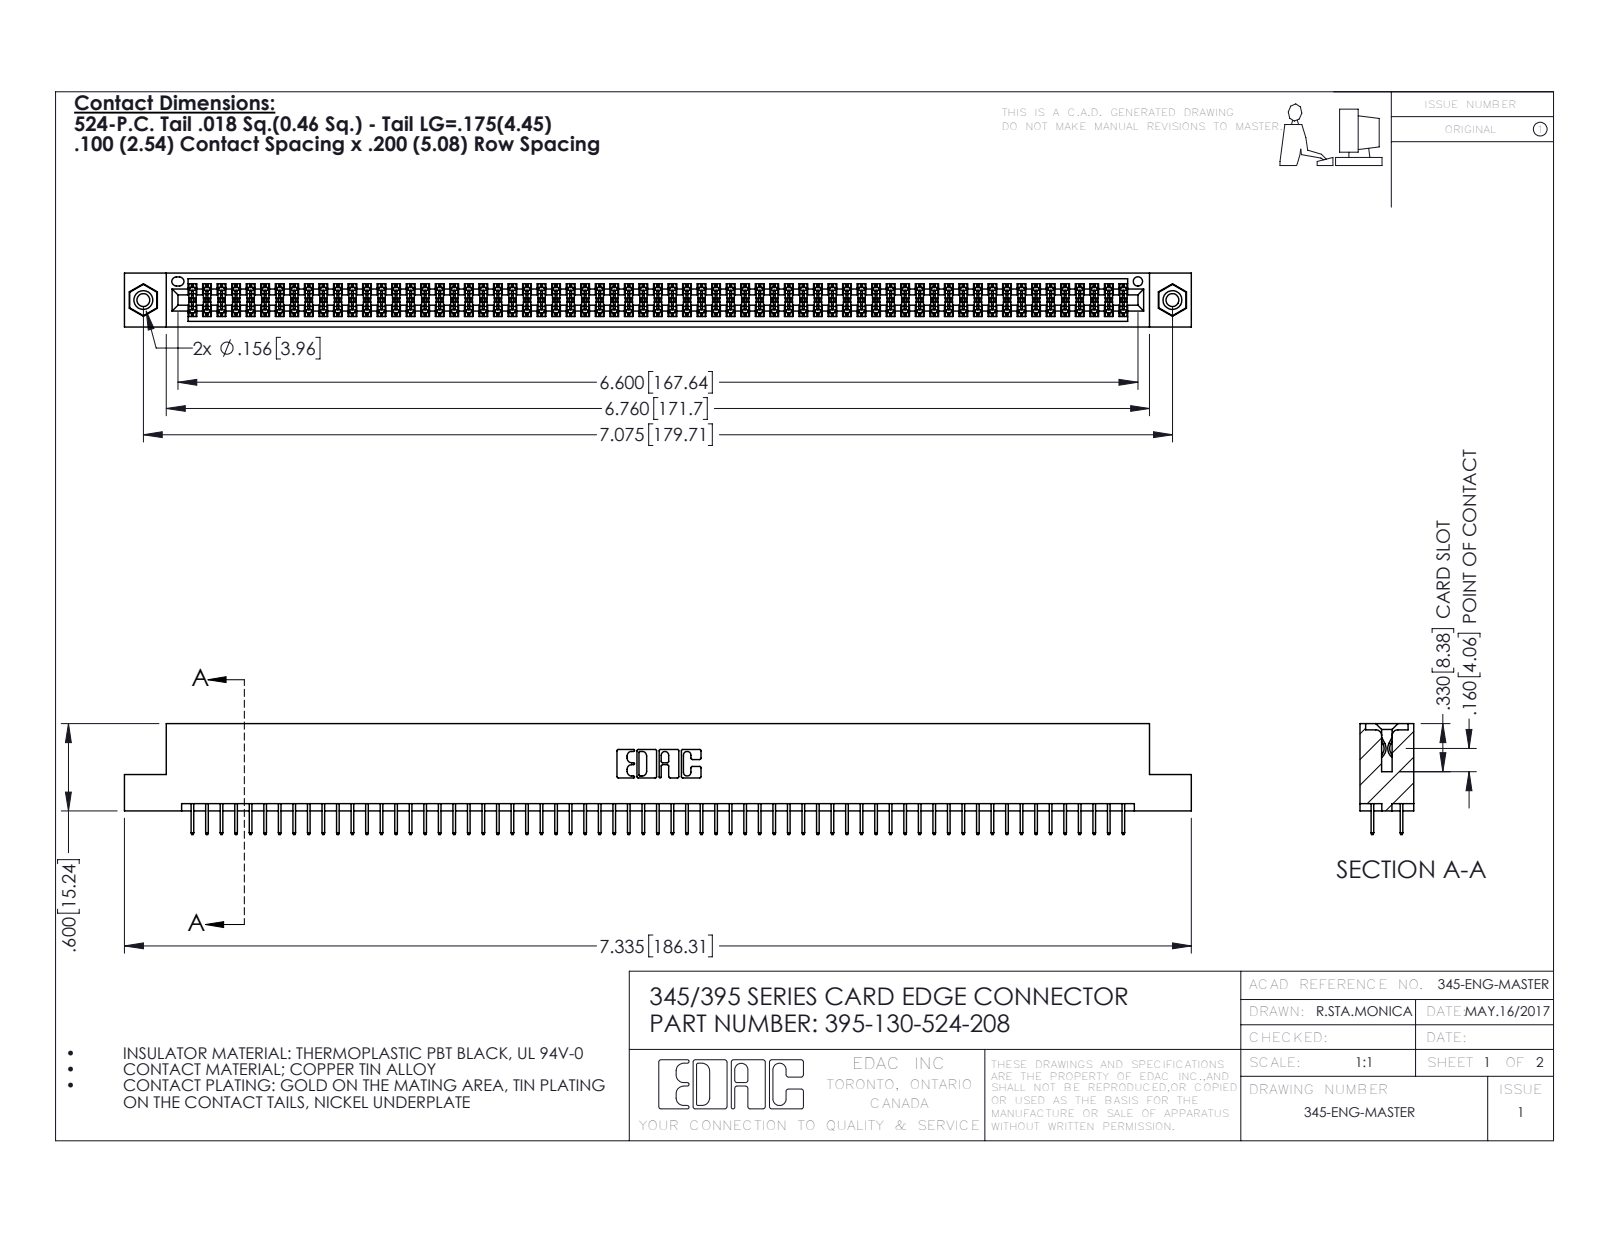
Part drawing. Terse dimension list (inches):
name: 395-130-524-208; 345-292-001_345-293-124; 345-250-001_345-250-003-102; 345 Part_Flush Mounting Lugs - 0.156 Dia-TI
written by: SolidWorks 2016 (CONFIG_CONTROL_DESIGN)
unit: in
bodies: 133 solids, 7206 faces (5182 planar, 2008 cylindrical, 16 other)
size: 7.335 × 0.762 × 0.37
volume: 1.105 in³; area: 41.4 in²
holes: 2× ⌀0.089, 2× ⌀0.125, 2× ⌀0.156, 1× ⌀0.064
bosses: 2× ⌀0.155
rounds: 195× R0.006, 22× R0.01, 6× R0.007, 6× R0.031, 3× R0.026, 2× R0.014, 2× R0.019, 2× R0.022
face distances: 0.072, 0.298, 0.2, 0.37, 0.098, 0.272, 0.025, 0.225, 0.072, 0.175
hole spacings: 0.27, 6.839, 7.075
